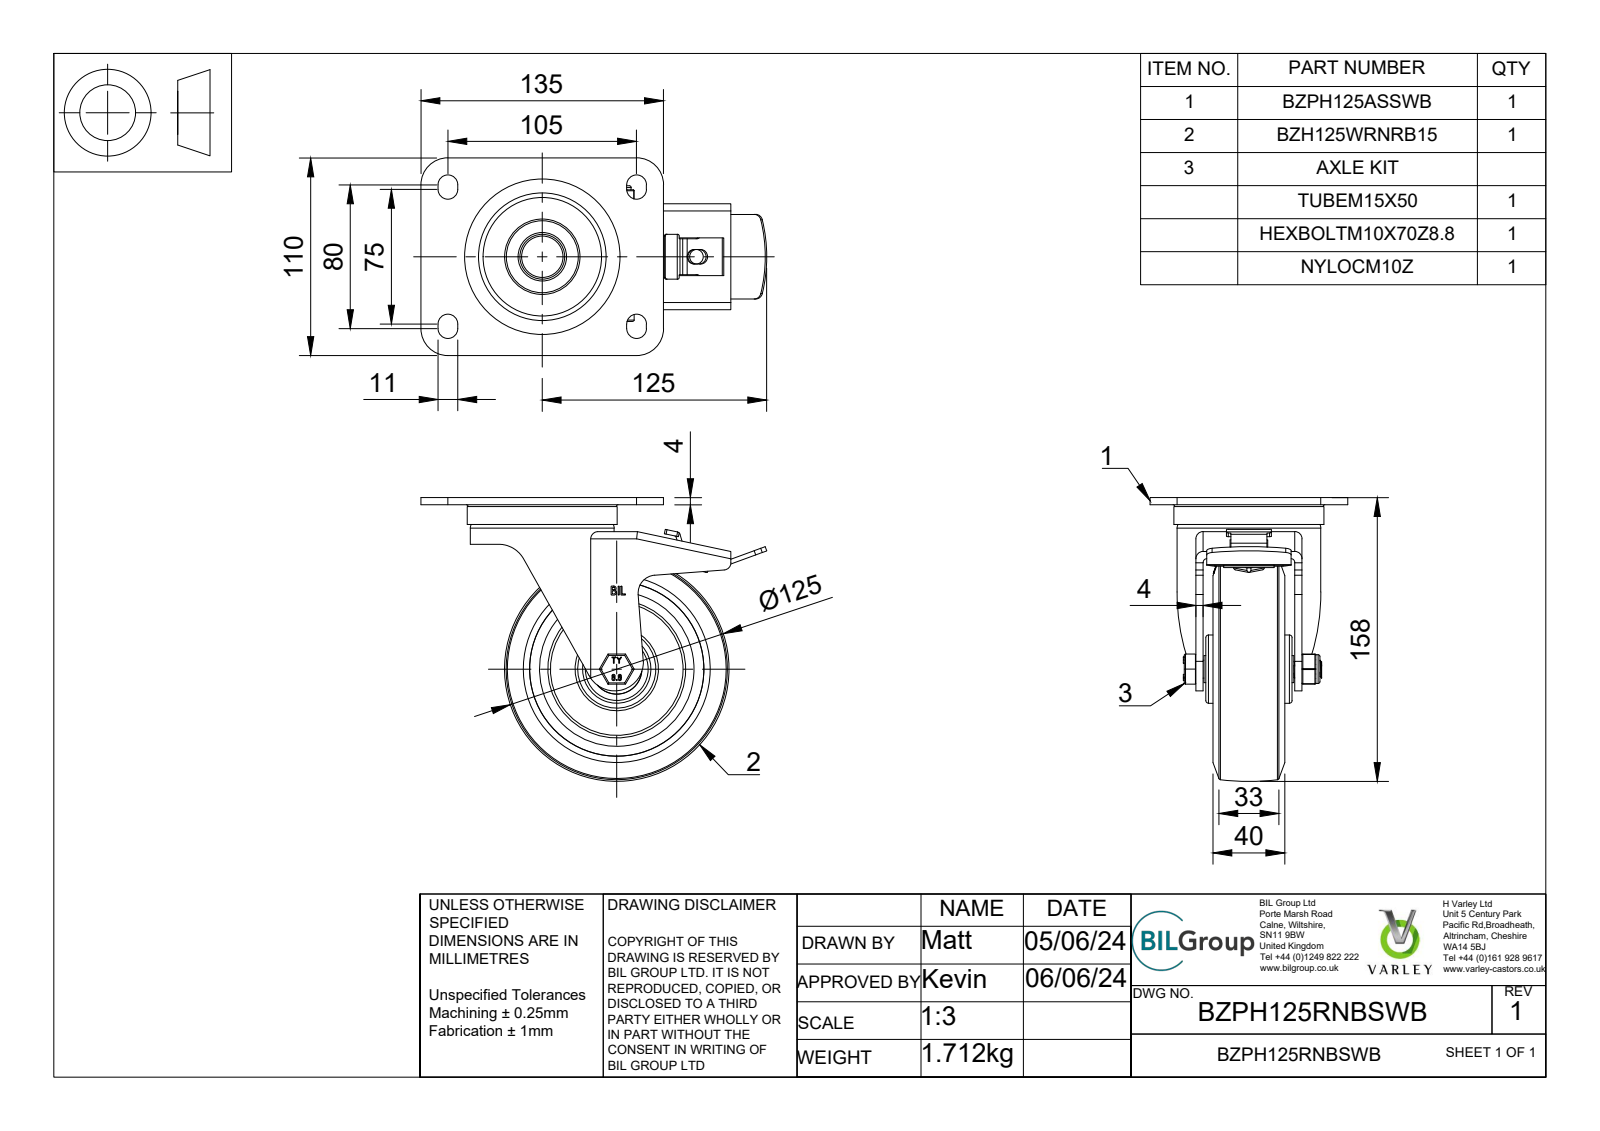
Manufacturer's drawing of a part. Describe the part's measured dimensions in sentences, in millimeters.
The part is named "BZPH125RNBSWB v3; BZPH125ASSWB v1; ZINC PLATED, PRESSED STEEL TOP PLATE; ZINC PLATED, PRESSED STEEL FORKS (+8 more)". Its 3-D file was written by "Autodesk Translation Framework v13.14.0.145 (AUTOMOTIVE_DESIGN)". It is 23 solids with 764 faces: 431 planar, 208 cylindrical and 125 other. Overall it measures 192.5 by 158 by 110 millimeters. Its volume is 545 330 cubic millimeters and its surface area 194 601 square millimeters. Round holes: 1 of diameter 8, 1 of diameter 10, 1 of diameter 10.2, 1 of diameter 10.5, 1 of diameter 12, 1 of diameter 15, 1 of diameter 17, 1 of diameter 23, 1 of diameter 26, 1 of diameter 28, 1 of diameter 32, 1 of diameter 60. Round bosses or shafts: 8 of diameter 4, 1 of diameter 83.5, 1 of diameter 80, 1 of diameter 51, 1 of diameter 38, 1 of diameter 28, 1 of diameter 27.9, 1 of diameter 25. Partial cylindrical surfaces (rounded edges, fillets, slot ends): 26 of radius 0.5, 12 of radius 4, 10 of radius 1.5, 8 of radius 5.5, 7 of radius 2, 6 of radius 0.75, 6 of radius 1, 5 of radius 6. The main face-to-face distances are 4, 13, 9, 5.5, 49.5, 15, 1, 9.5, 55, 20.5.
